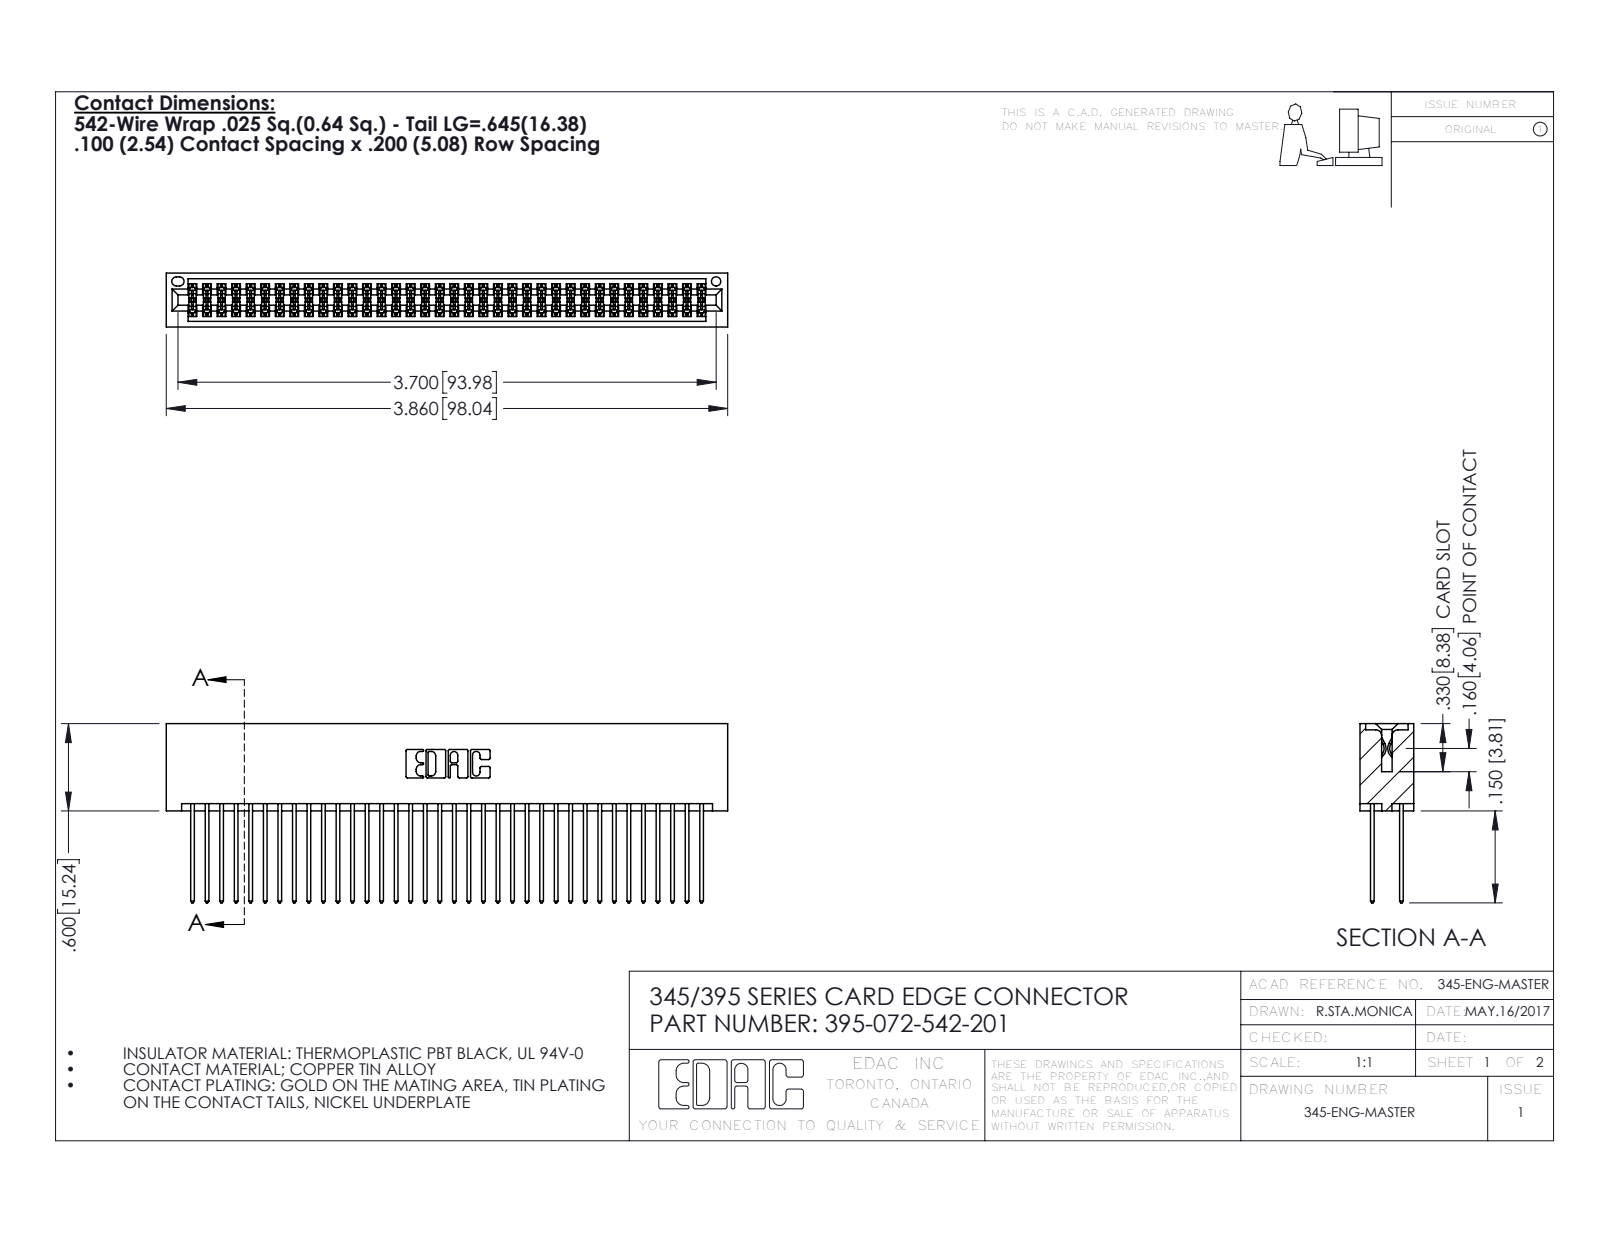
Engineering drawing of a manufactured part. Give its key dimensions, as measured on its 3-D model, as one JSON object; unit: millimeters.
{"part_name": "345 Part_No Mounting Lugs; 395-072-542-201; 345-292-001_345-293-142", "step_written_by": "SolidWorks 2016 (CONFIG_CONTROL_DESIGN)", "units": "millimeters", "bodies": {"solids": 73, "faces": 3718, "planar": 2452, "cylindrical": 1266, "other": 0}, "overall_size": [98, 31.3, 9.4], "volume_mm3": 10400, "surface_area_mm2": 17150, "round_holes": [[1.6, 1]], "partial_cylinders_radius": [[0.2, 108], [0.3, 72], [0.3, 22], [0.2, 6], [0.8, 6], [0.7, 3], [0.4, 2], [0.5, 2]], "face_to_face_distances": [7.6, 1.8, 5.1, 2.5, 6.9, 0.6, 5.7, 9.4, 4.4, 3.8]}
